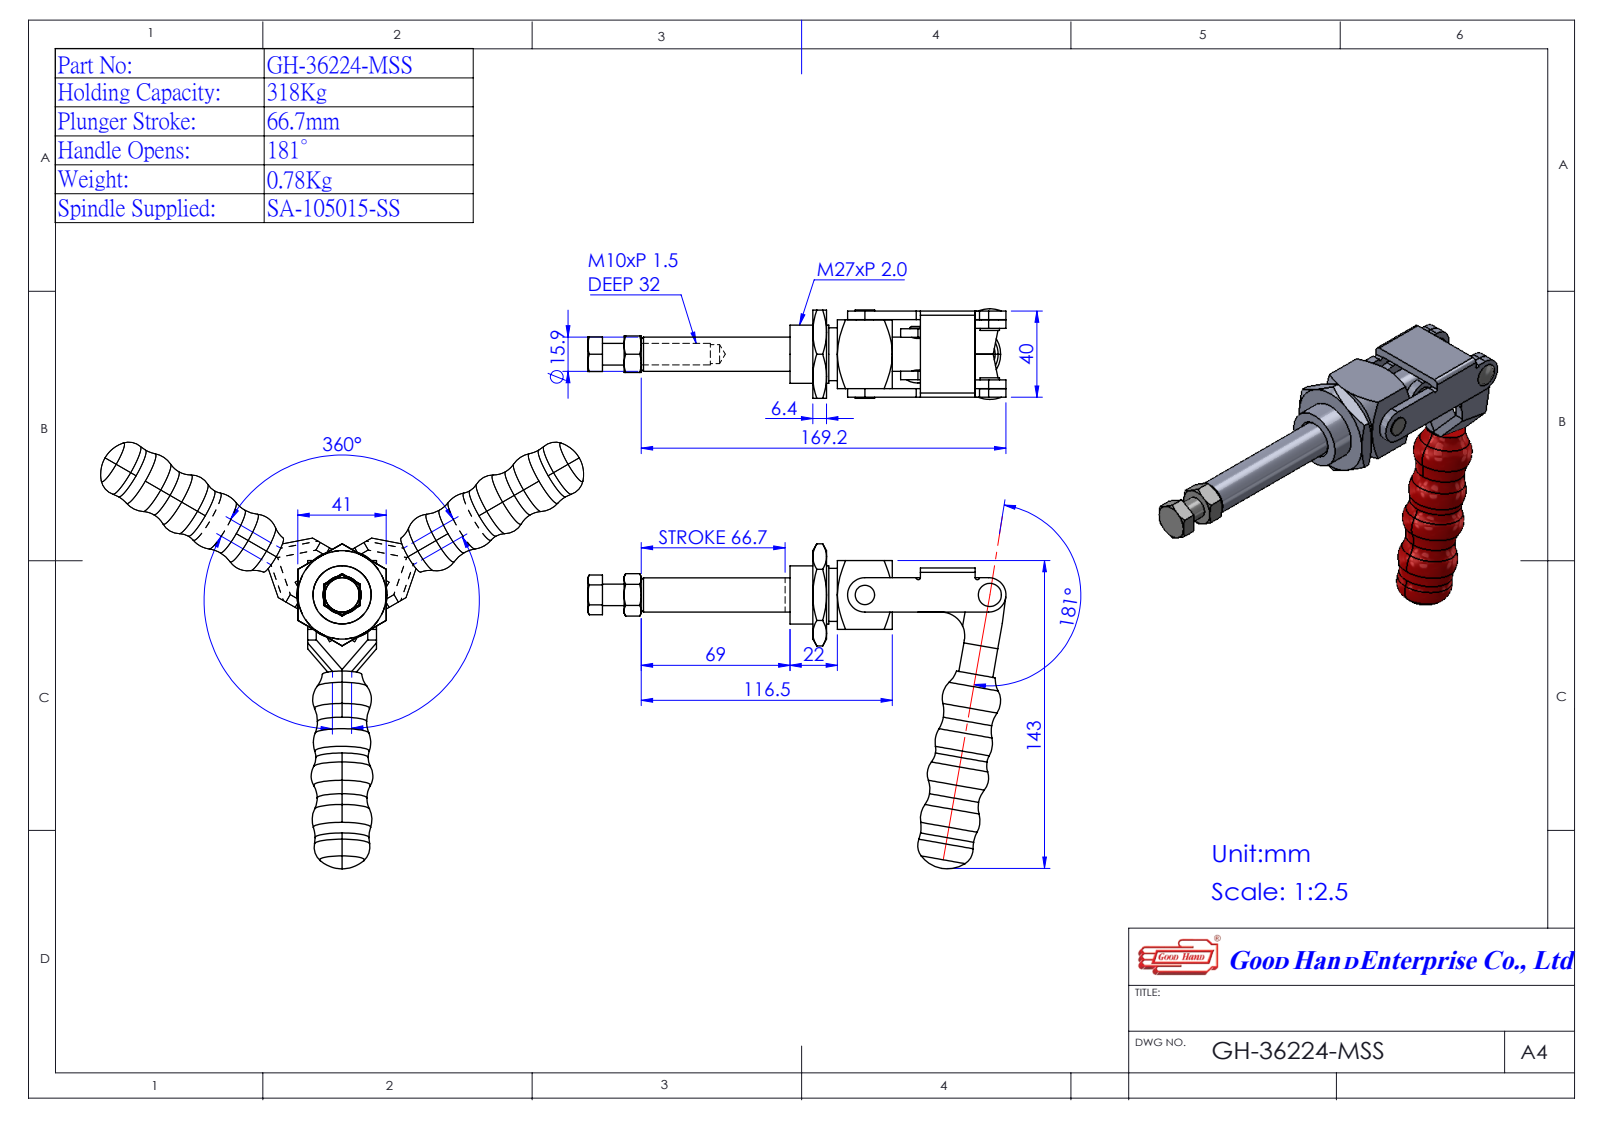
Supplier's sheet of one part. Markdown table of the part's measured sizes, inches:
| quantity | value |
| --- | --- |
| part name | GH-36224-MSS; Group2^493793(GH-36224M); Group4^493793(GH-36224M); Group1^493793(GH-36224M) (+1 more) |
| STEP written by | SolidWorks 2016 (AUTOMOTIVE_DESIGN) |
| units | inches |
| bodies | 4 solids, 198 faces (84 planar, 65 cylindrical, 49 other) |
| overall size | 7.532 × 5.966 × 1.65 |
| volume | 8.081 in³ |
| surface area | 66.95 in² |
| round holes (diameter × count) | 0.236 × 3, 0.626 × 1 |
| round bosses / shafts (diameter × count) | 1.063 × 1, 0.63 × 1, 0.394 × 1, 0.354 × 1 |
| partial cylindrical surfaces (radius × count) | 0.315 × 3, 0.02 × 2, 0.039 × 2, 0.433 × 1 |
| main face-to-face distances | 0.157, 1.256, 1.413, 1.571, 0.319, 1.094, 0.161, 0.937, 1.098, 0.315 |
| hole center spacings | 0.969, 1.315, 2.283 |
